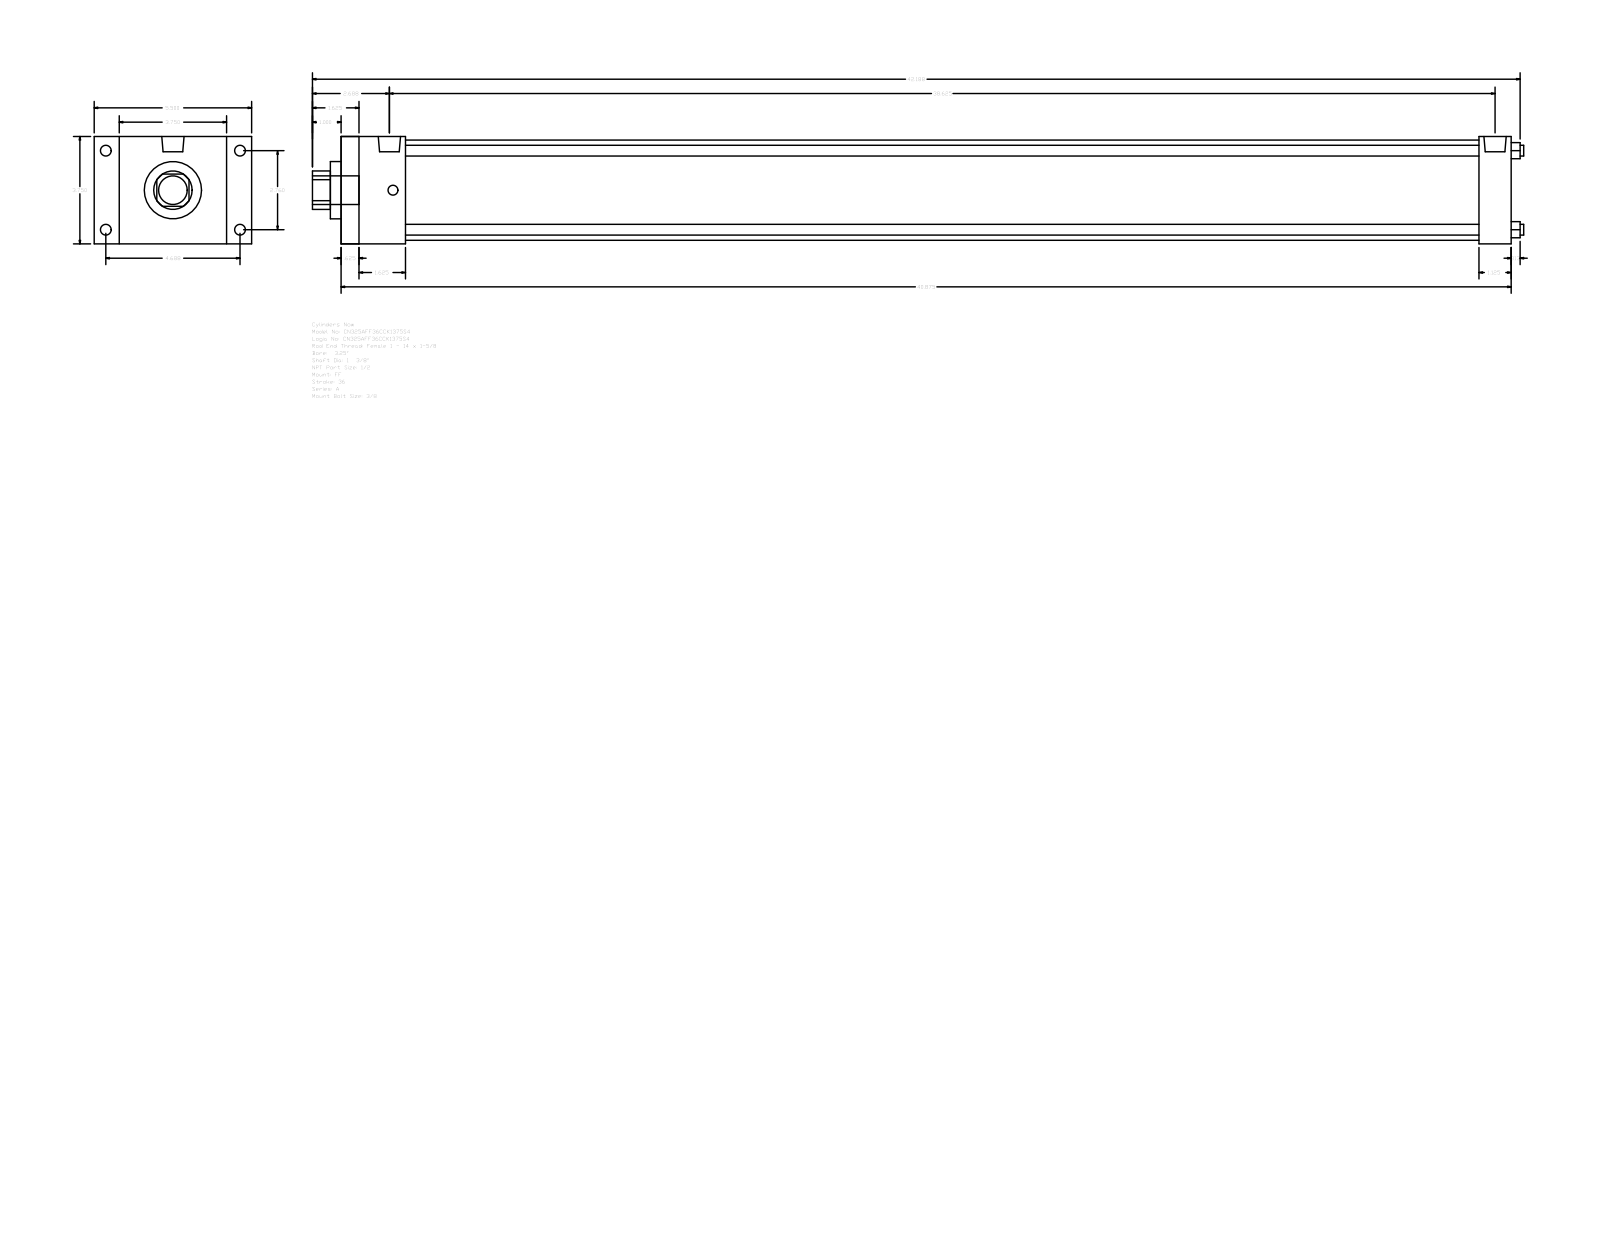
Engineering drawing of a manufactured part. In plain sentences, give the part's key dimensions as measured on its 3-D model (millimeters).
The part is named "A_FF__0325_1.375". Its 3-D file was written by "GSSL Pune (CONFIG_CONTROL_DESIGN)". It is 0 solids with 92 faces: 64 planar, 28 cylindrical and 0 other. Overall it measures 1074.74 by 139.7 by 95.25 millimeters. Round holes: 4 of diameter 9.53, 1 of diameter 34.92, 1 of diameter 50.8, 1 of diameter 88.9. Round bosses or shafts: 4 of diameter 9.53, 4 of diameter 8.73, 2 of diameter 19.77, 1 of diameter 25.4. Partial cylindrical surfaces (rounded edges, fillets, slot ends): 1 of radius 17.06. The main face-to-face distances are 95.24, 1038.22, 1022.35, 15.87, 22.23, 117.47, 28.57, 57.15, 1009.65, 41.28. The hole center spacings are 49.57, 70.1, 99.14.
